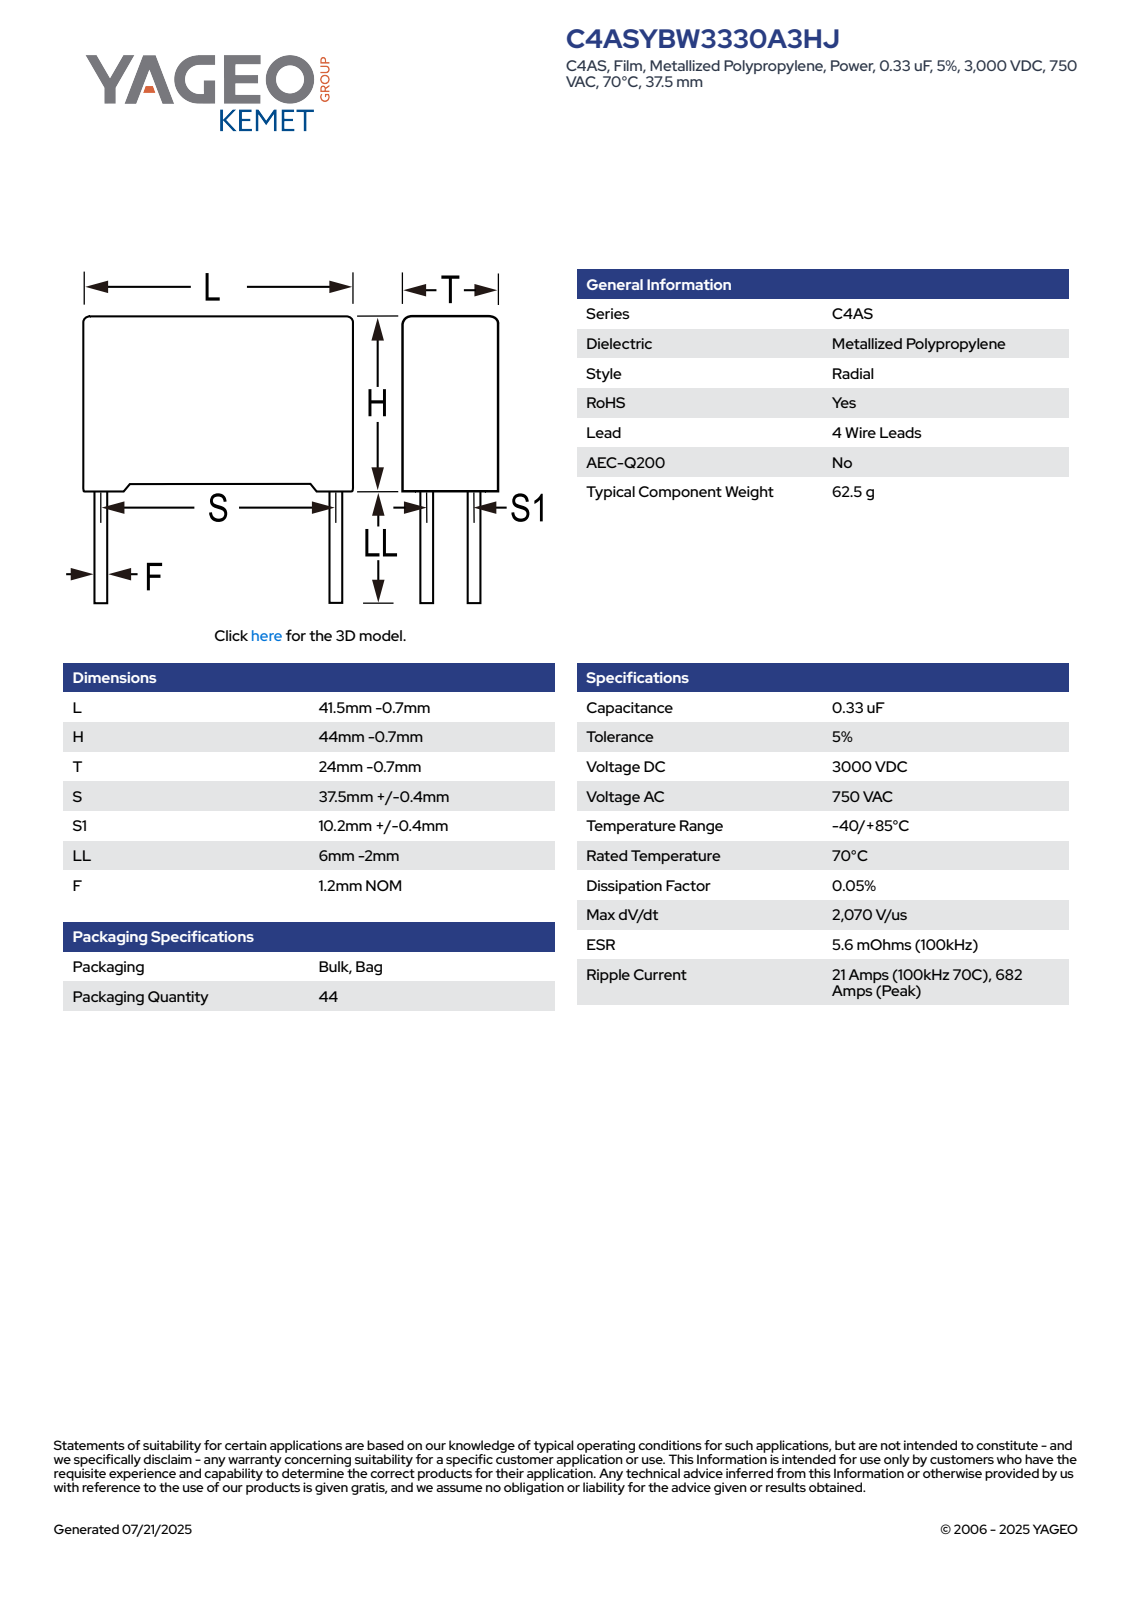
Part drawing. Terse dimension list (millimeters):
name: CFP_RB4_41.5X44X24_L40.8H43.3T23.3S37.5S110.2LL4F1.2
written by: SolidWorks 2014 (AUTOMOTIVE_DESIGN)
unit: mm
bodies: 4 solids, 91 faces (83 planar, 8 cylindrical, 0 other)
size: 47.3 × 40.8 × 23.3
volume: 40 097 mm³; area: 7 637 mm²
bosses: 4× ⌀1.2
face distances: 23.3, 40.8, 42.03, 1.27, 43.3, 1.43, 23.31, 39.37, 21.87, 37.94
